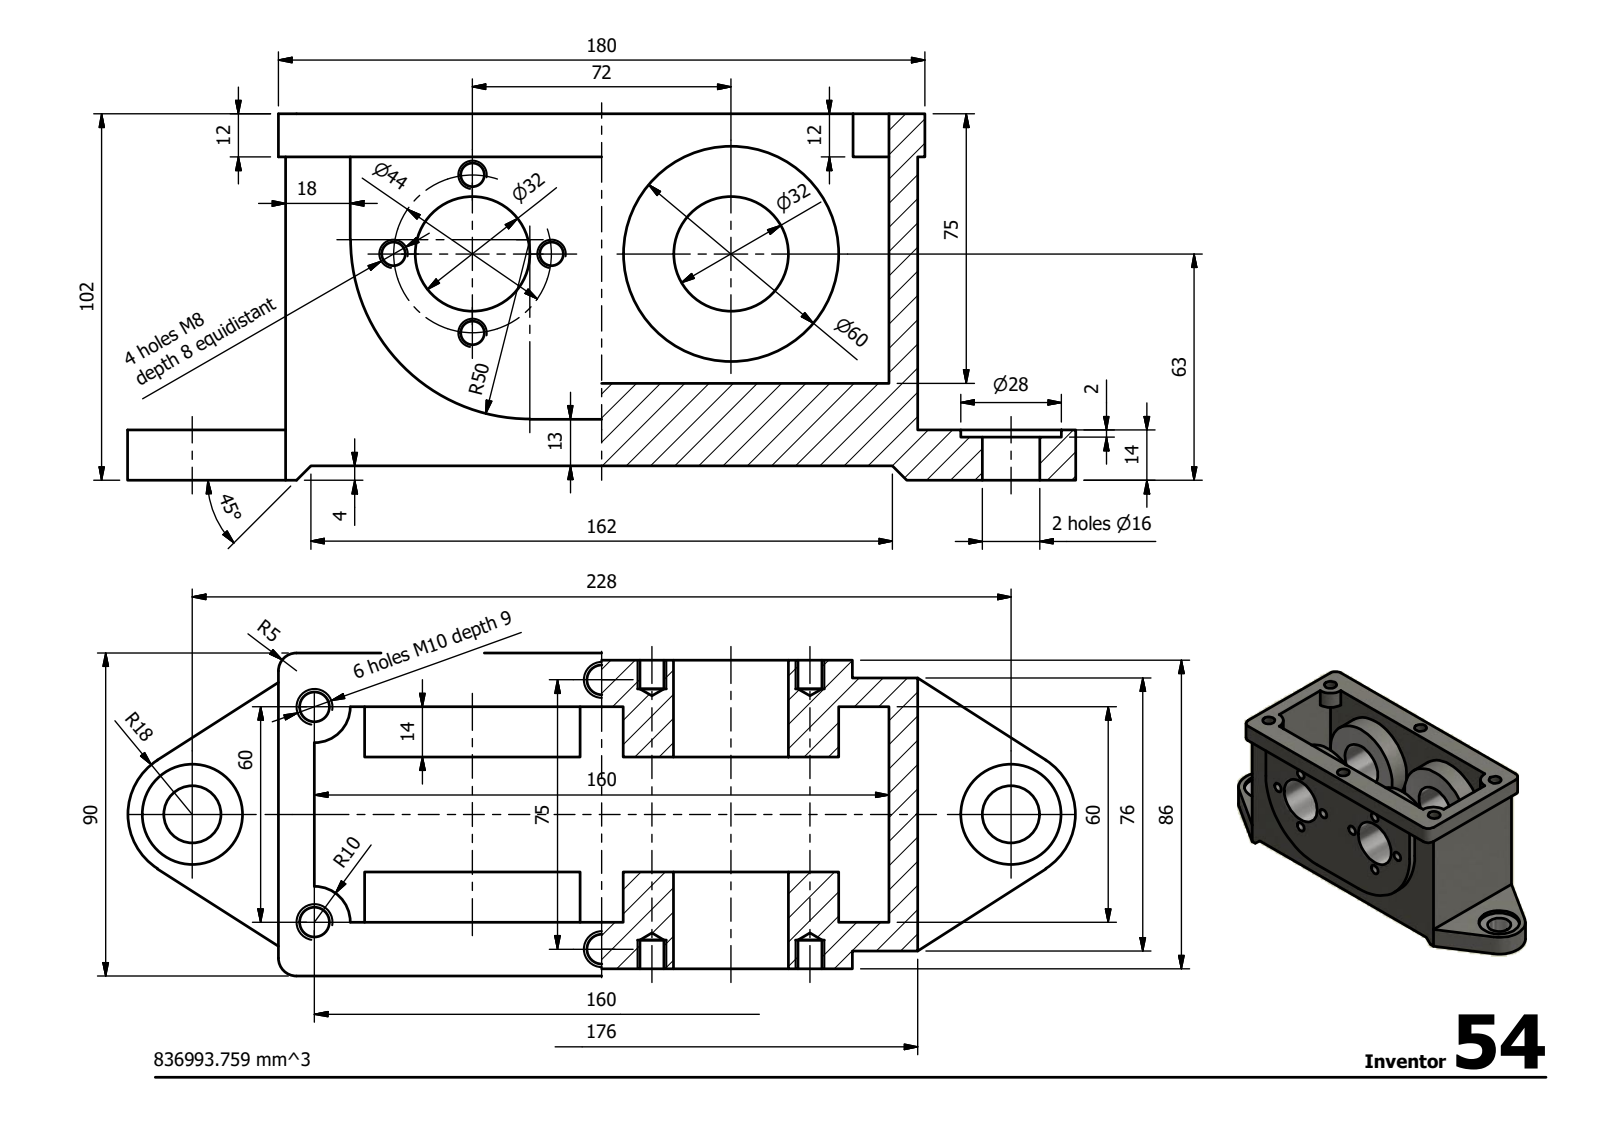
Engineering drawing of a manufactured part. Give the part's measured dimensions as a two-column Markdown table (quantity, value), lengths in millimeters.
| quantity | value |
| --- | --- |
| STEP written by | Autodesk Inventor 2014 (AUTOMOTIVE_DESIGN) |
| units | millimeters |
| bodies | 1 solid, 114 faces (44 planar, 48 cylindrical, 22 other) |
| overall size | 264 × 102 × 90 |
| volume | 836 994 mm³ |
| surface area | 147 002 mm² |
| round holes (diameter × count) | 6.65 × 8, 8.38 × 6, 16 × 2, 28 × 2, 32 × 2 |
| round bosses / shafts (diameter × count) | 60 × 2 |
| partial cylindrical surfaces (radius × count) | 5 × 4, 10 × 4, 18 × 2, 50 × 2 |
| main face-to-face distances | 8, 13, 73, 5, 27, 81, 68, 14, 75, 23 |
| hole center spacings | 22, 31.11, 72, 44, 54.63, 75.29, 96.54, 120.01 |
